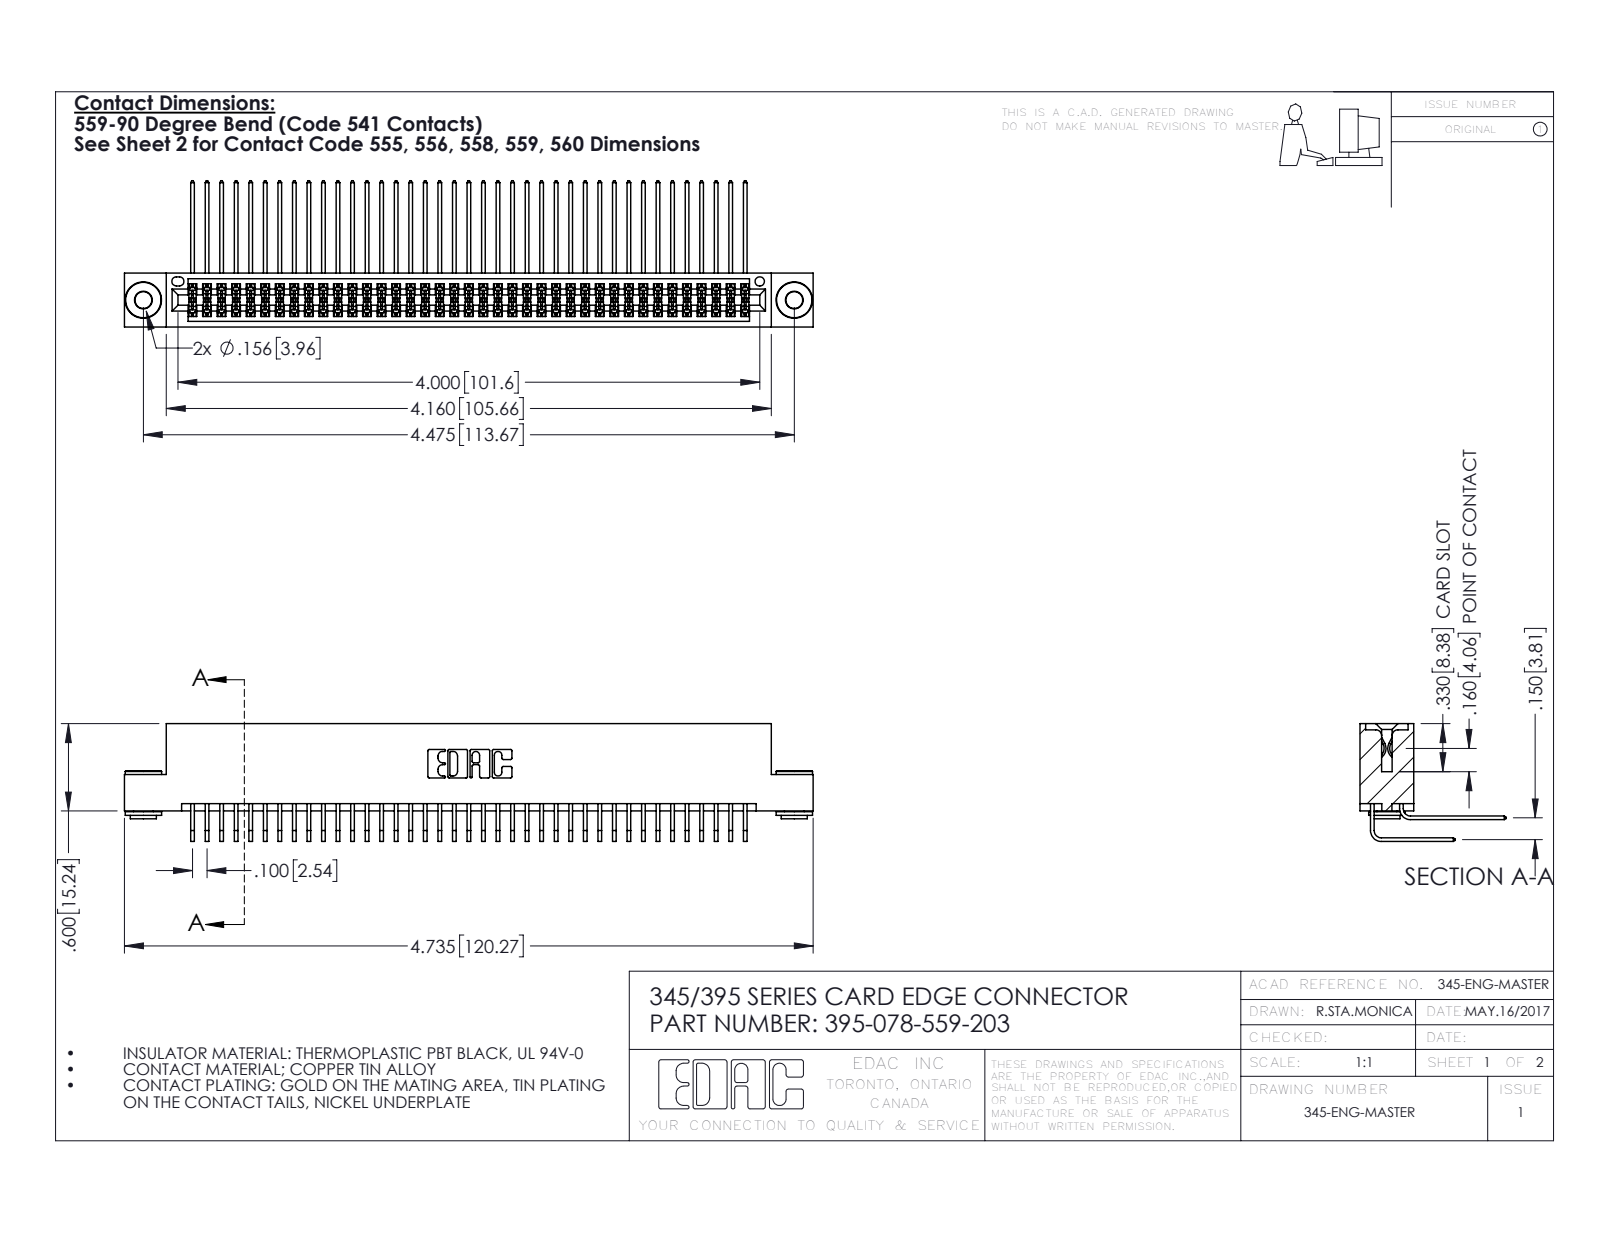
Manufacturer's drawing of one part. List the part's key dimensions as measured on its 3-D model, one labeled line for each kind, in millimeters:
Part name (STEP PRODUCT): 345-292-001_558 559 Tail - 1; 395-078-559-203; 345 Part_Flush Mounting Lugs - 0.156 Dia-TH; 345-292-001_559 Tail - 2 (+1 more)
STEP written by: SolidWorks 2016 (CONFIG_CONTROL_DESIGN)
Units: millimetres
Bodies: 81 solids, 4220 faces (2820 planar, 1392 cylindrical, 8 other)
Overall size (bounding box): 120.3 × 25.5 × 20.5
Volume: 12 100 mm³ · Surface area: 20 190 mm²
Round holes (diameter × count): ⌀2.9 ×2, ⌀4 ×2, ⌀1.6 ×1
Round bosses / shafts (diameter × count): ⌀6.4 ×2, ⌀4.6 ×2, ⌀3.5 ×2
Partial cylindrical surfaces — rounded edges, fillets, slot ends (radius × count): R0.2 ×117, R0.3 ×22, R0.2 ×6, R0.8 ×6, R0.7 ×3, R0.4 ×2, R0.5 ×2, R0.6 ×2
Main face-to-face distances: 1.8, 7.6, 5.1, 9.4, 0.6, 2.5, 6.9, 5.7, 4.4, 3.8
Hole centre spacings: 6.9, 107.7, 113.7
